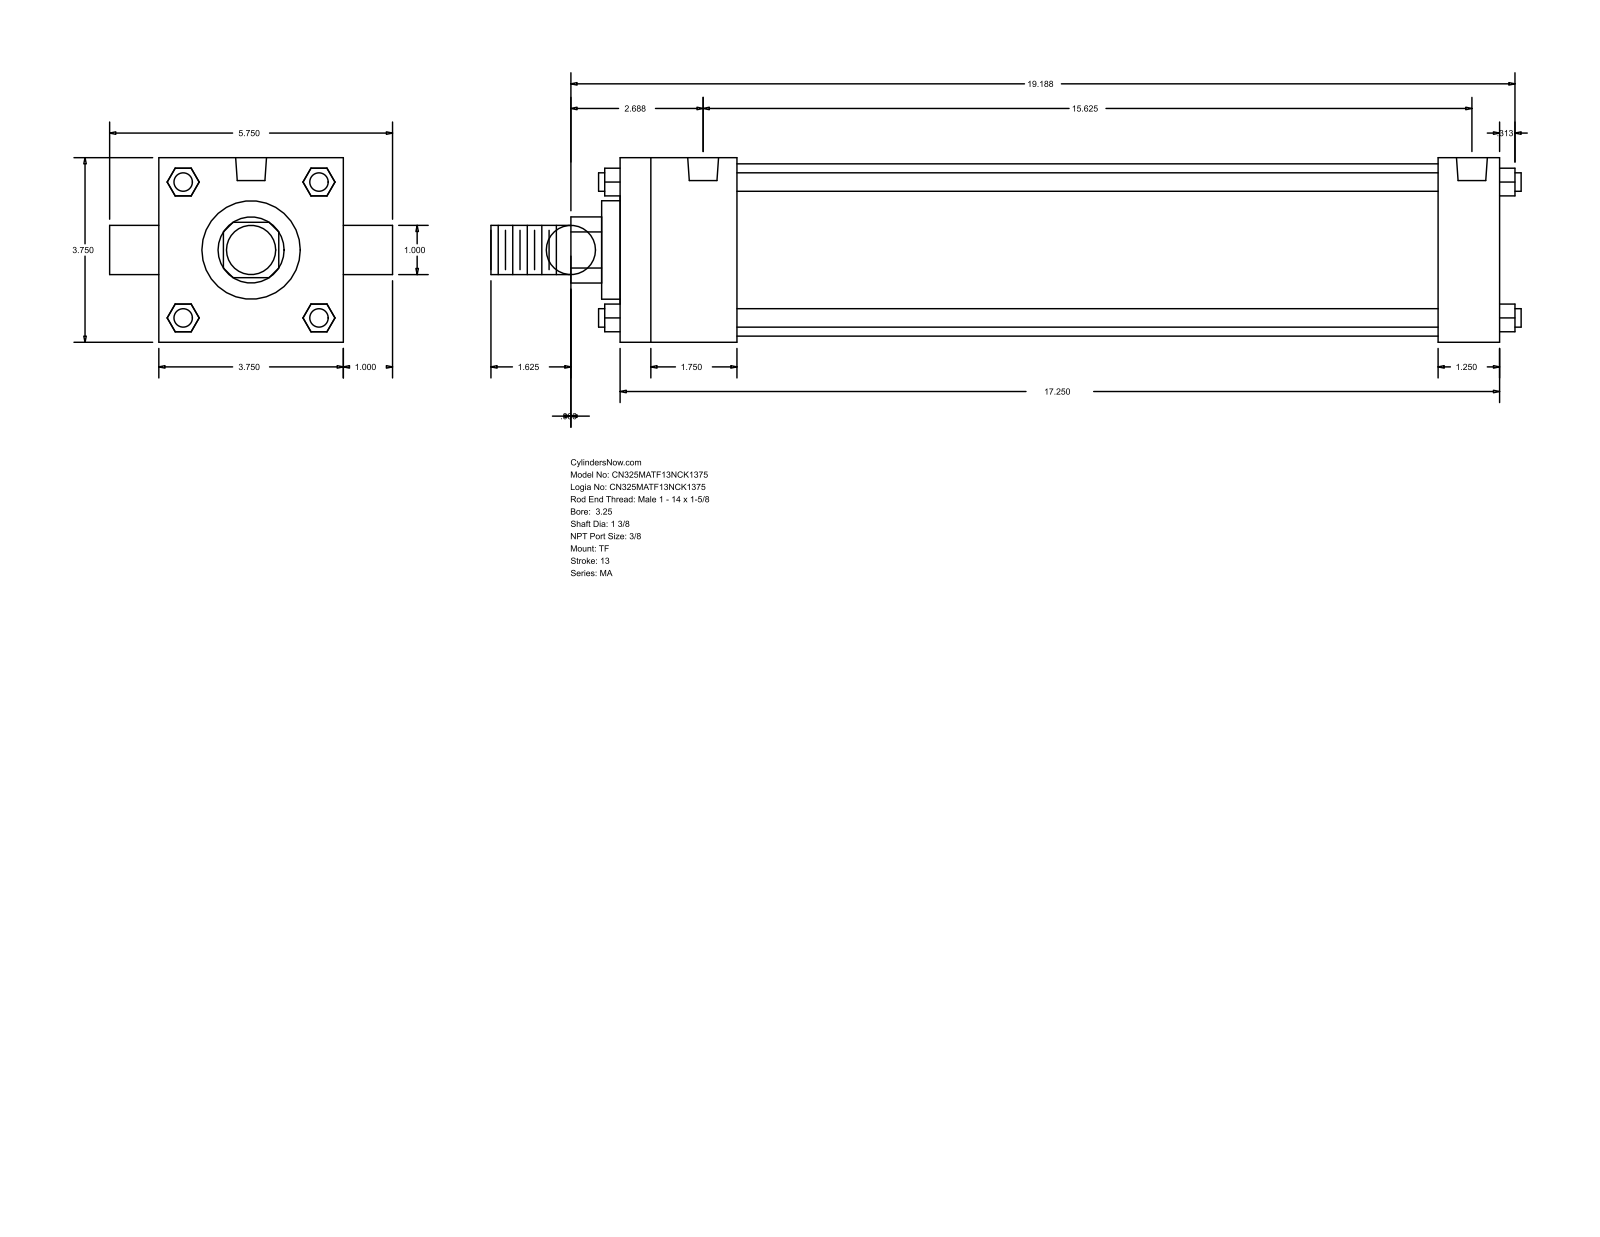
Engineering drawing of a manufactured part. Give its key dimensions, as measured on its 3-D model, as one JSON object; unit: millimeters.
{"part_name": "MA_TF__0325_1.375", "step_written_by": "GSSL Pune (CONFIG_CONTROL_DESIGN)", "units": "millimeters", "bodies": {"solids": 0, "faces": 120, "planar": 92, "cylindrical": 28, "other": 0}, "overall_size": [531.81, 146.05, 95.25], "round_holes": [[11.11, 3], [15.93, 2]], "round_bosses_or_shafts": [[9.53, 4], [25.4, 2], [88.9, 1], [50.8, 1], [34.92, 1]], "partial_cylinders_radius": [[17.06, 1]], "face_to_face_distances": [95.24, 454.03, 60.32, 422.28, 361.96, 393.71, 31.75, 9.52, 69.84, 431.8], "hole_center_spacings": [4.76, 4.77, 387.35, 392.11, 392.12, 396.88]}
